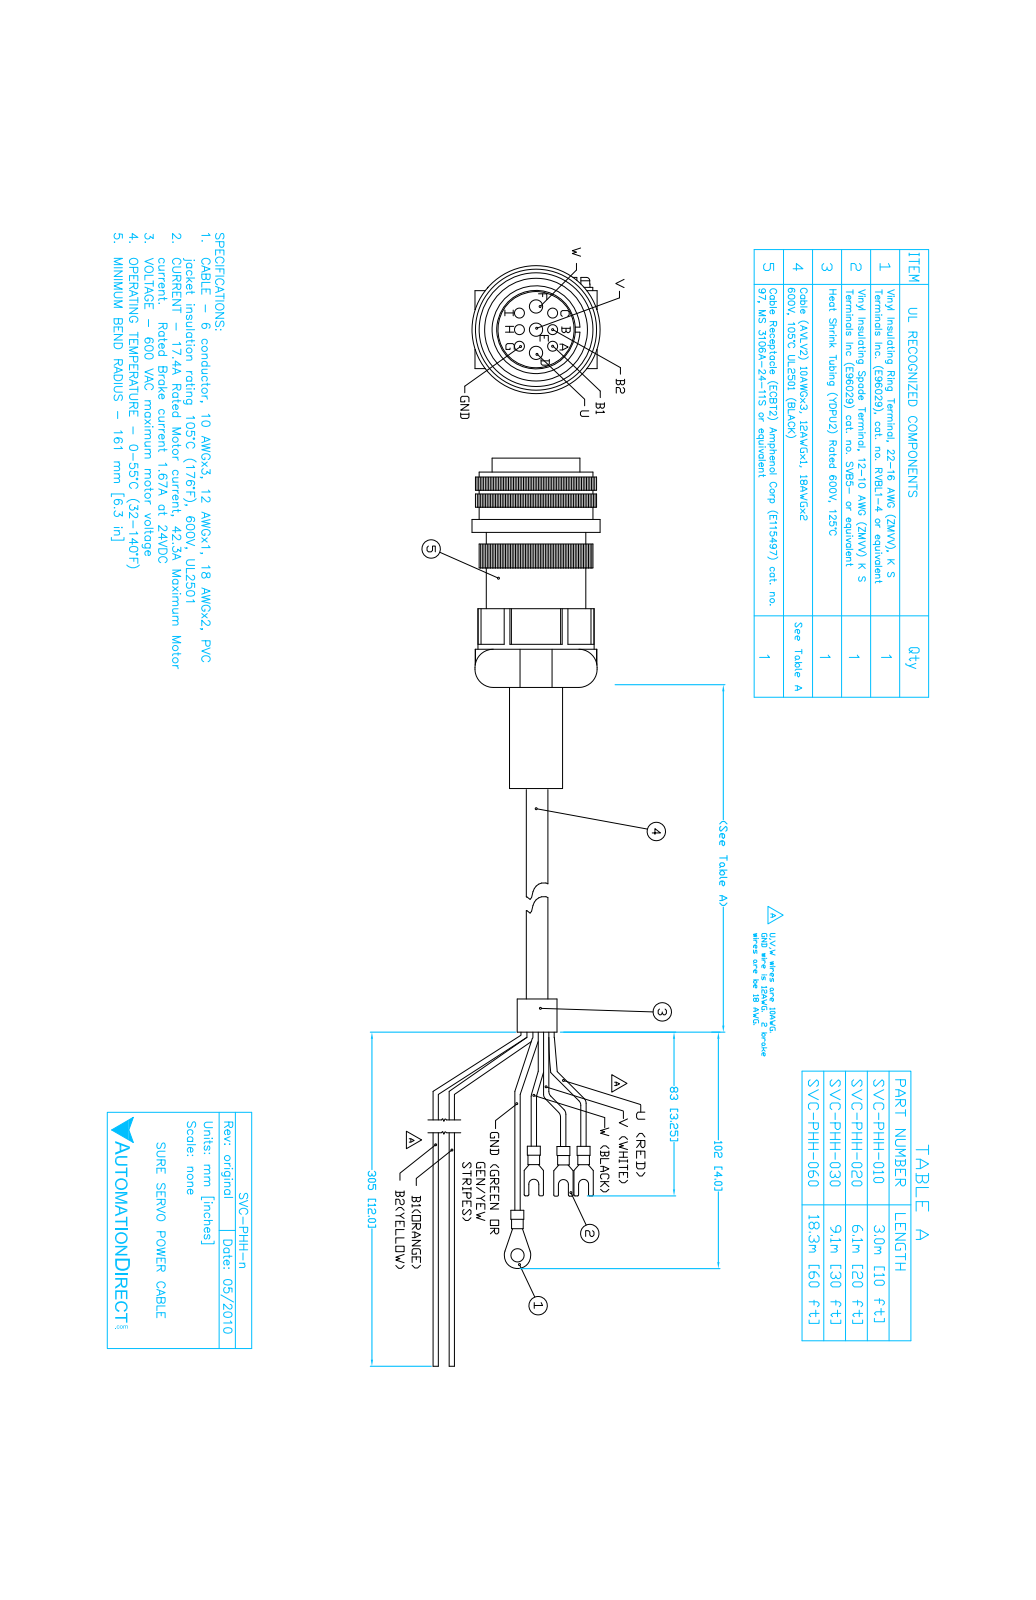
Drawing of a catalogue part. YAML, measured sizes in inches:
part_name: "SVC-PHH-060"
step_written_by: "SolidWorks 2015 (AUTOMOTIVE_DESIGN)"
units: inches
bodies: {solids: 8, faces: 715, planar: 403, cylindrical: 194, other: 118}
overall_size: [6.89, 2.82, 1.701]
volume: 7.37
surface_area: 69.5
round_holes:
  - {diameter: 0.108, count: 6}
  - {diameter: 0.157, count: 5}
  - {diameter: 0.63, count: 1}
  - {diameter: 0.709, count: 1}
  - {diameter: 1.122, count: 1}
  - {diameter: 1.457, count: 1}
  - {diameter: 1.496, count: 1}
round_bosses_or_shafts:
  - {diameter: 0.256, count: 2}
  - {diameter: 1.701, count: 1}
  - {diameter: 1.654, count: 1}
  - {diameter: 1.622, count: 1}
  - {diameter: 1.583, count: 1}
  - {diameter: 1.427, count: 1}
  - {diameter: 1.299, count: 1}
  - {diameter: 1.102, count: 1}
partial_cylinders:
  - {radius: 0.256, count: 2}
  - {radius: 0.512, count: 1}
  - {radius: 0.787, count: 1}
  - {radius: 0.809, count: 1}
  - {radius: 0.821, count: 1}
face_to_face_distances: [2, 0.039, 0.63, 0.098, 1.768, 1.902, 0.059, 1.961, 1.091, 0.811]
hole_center_spacings: [0.246, 0.327, 0.392, 0.475, 0.658, 0.682, 0.61, 0.305]
